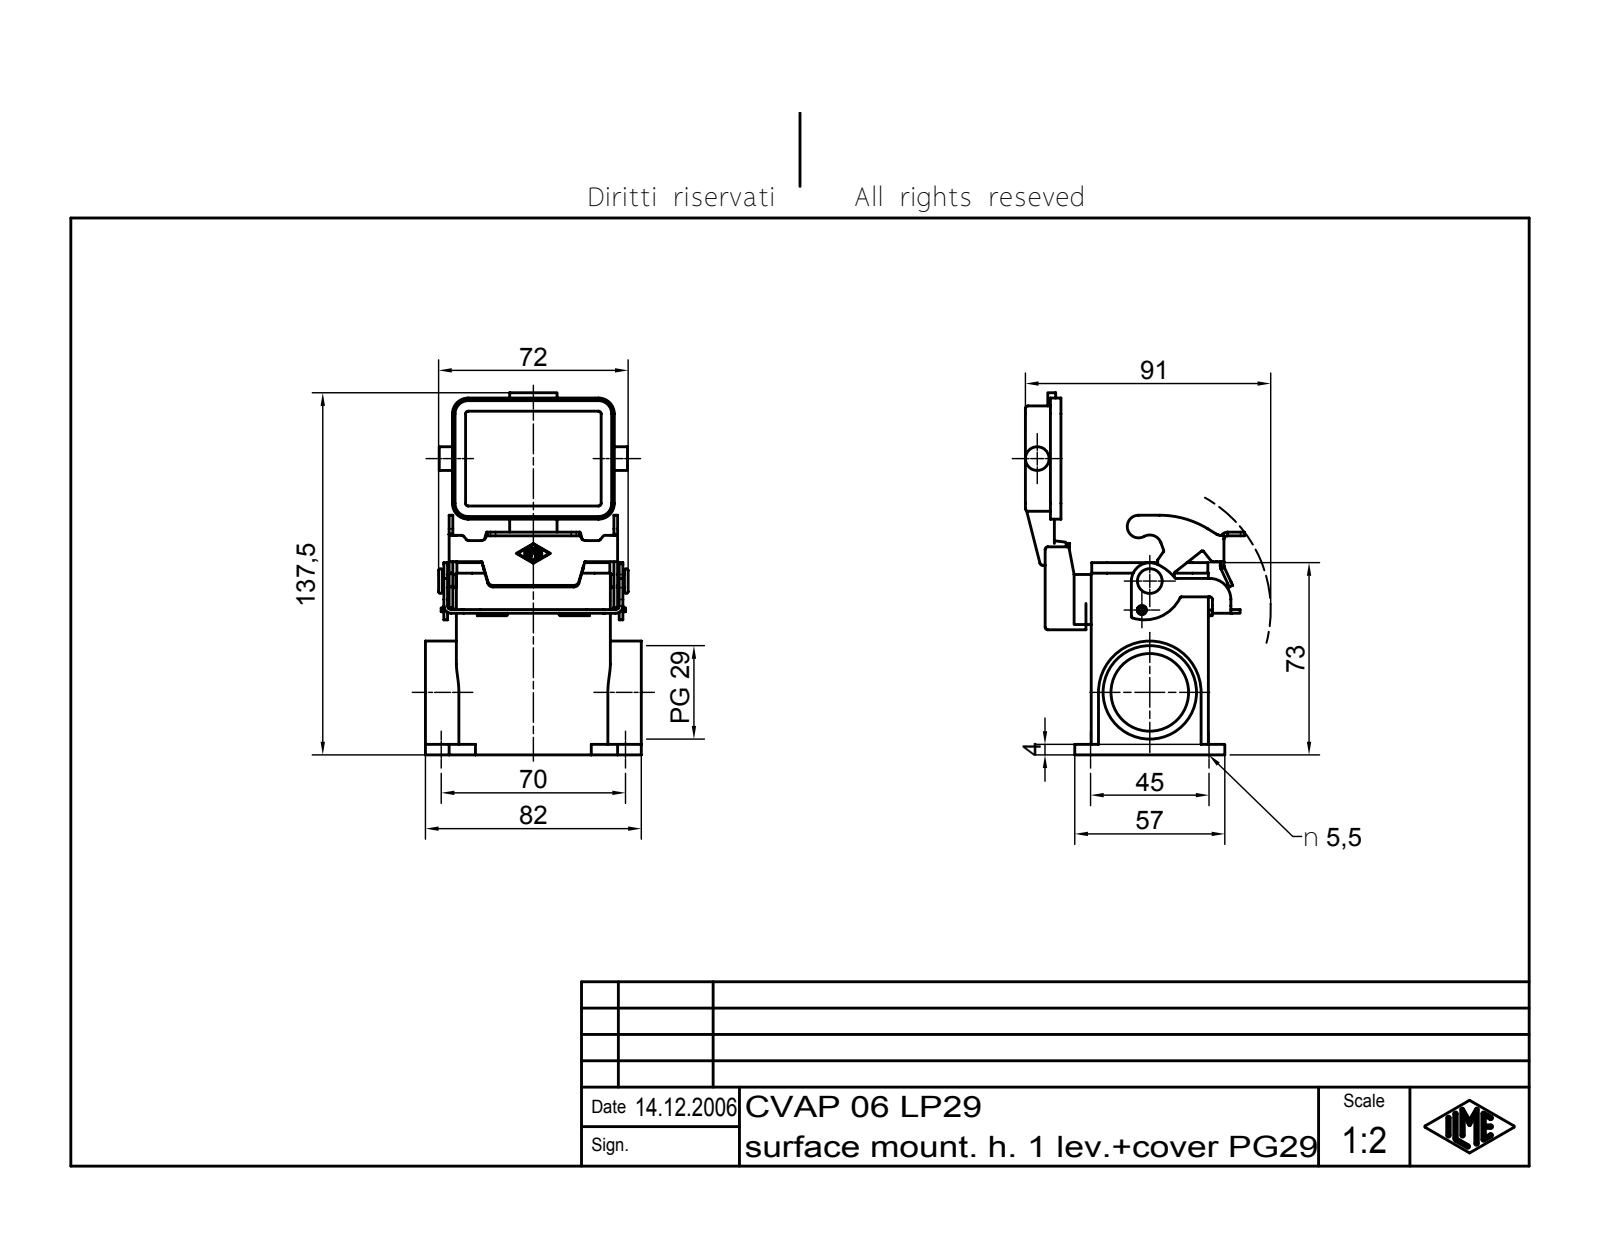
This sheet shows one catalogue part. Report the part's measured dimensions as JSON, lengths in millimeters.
{"part_name": "CVAP 06 LP29", "step_written_by": "Autodesk Inventor 7 (AUTOMOTIVE_DESIGN)", "units": "millimeters", "bodies": {"solids": 4, "faces": 590, "planar": 232, "cylindrical": 193, "other": 165}, "overall_size": [137.5, 83.23, 82], "volume_mm3": 110700, "surface_area_mm2": 64507, "round_holes": [[5.5, 4], [3.5, 1], [4, 1], [29.48, 1], [35.48, 1]], "round_bosses_or_shafts": [[5, 2], [9, 1], [7, 1], [3.2, 1], [3, 1]], "partial_cylinders_radius": [[1, 32], [0.25, 15], [0.5, 10], [1.5, 9], [6, 8], [2, 7], [1.4, 6], [2.8, 6]], "face_to_face_distances": [4, 40.5, 44.5, 2, 36.5, 10.75, 69.5, 13.5, 29, 65.5], "hole_center_spacings": [45, 70, 83.22, 31.4]}
